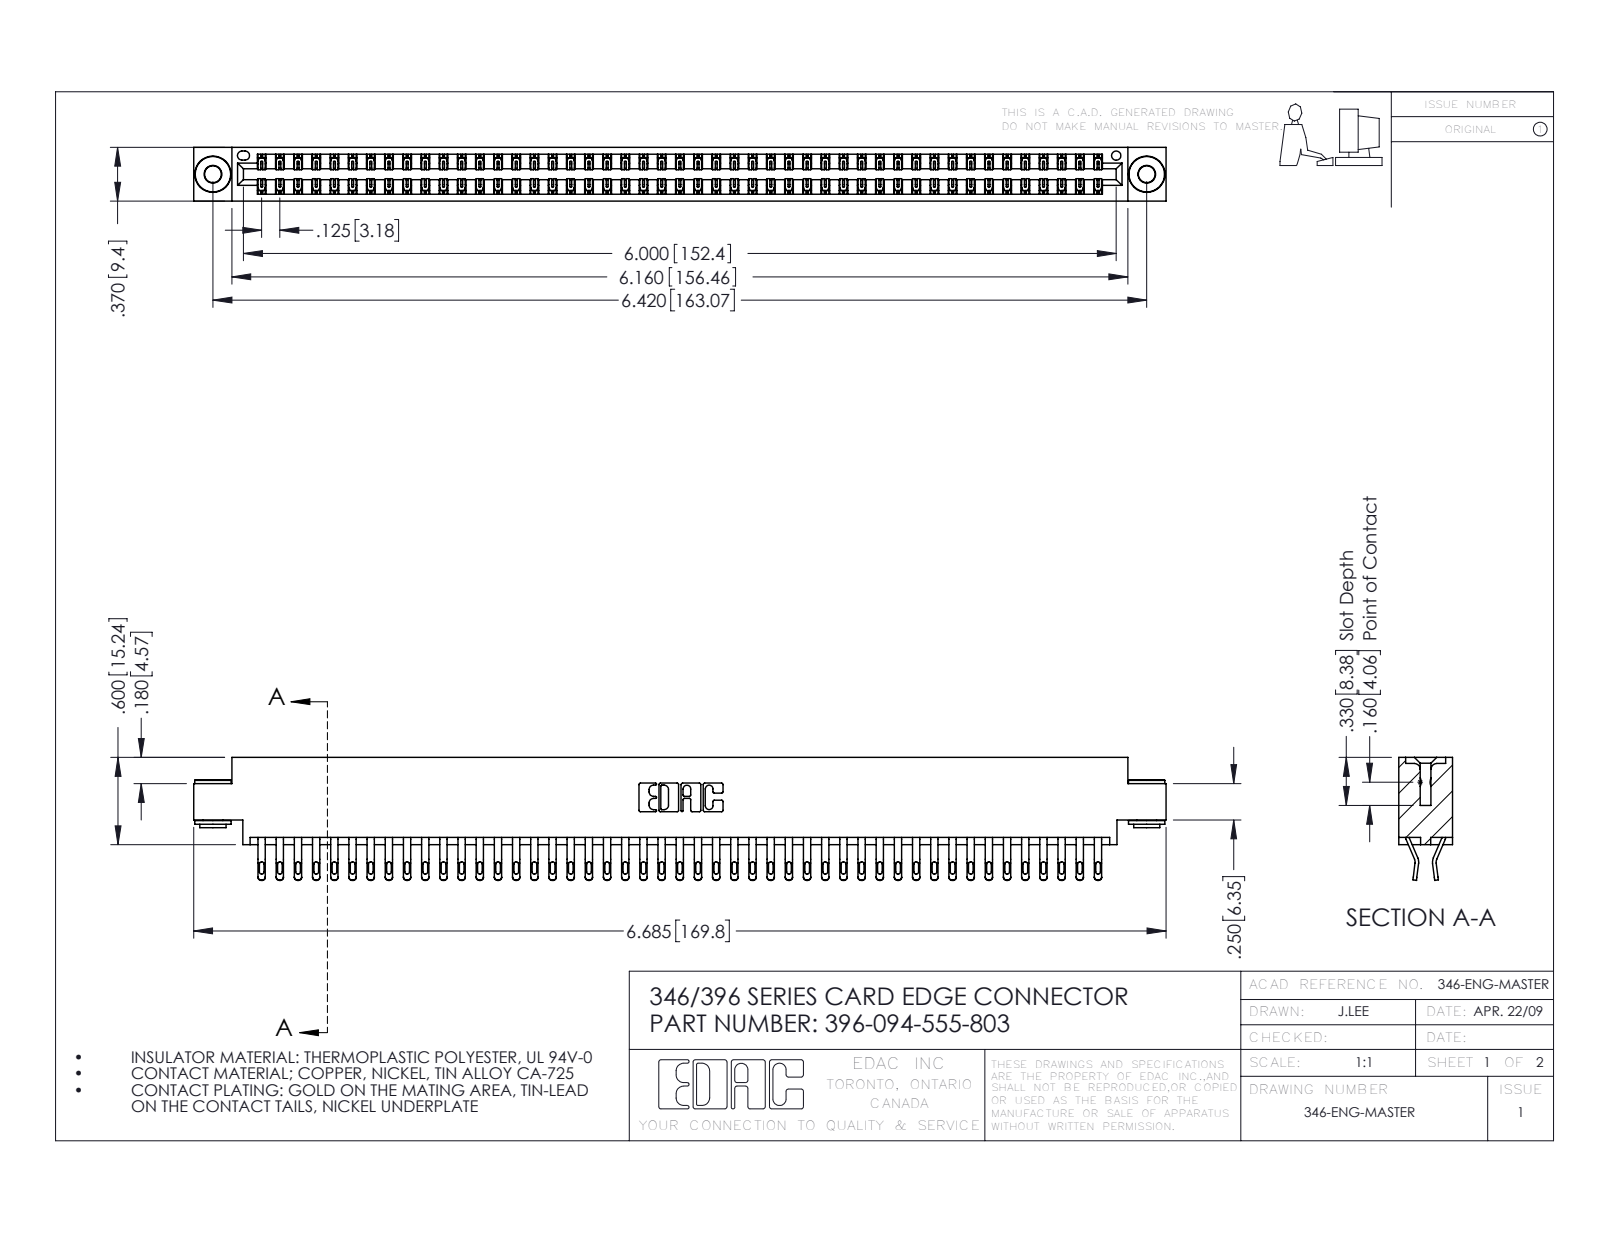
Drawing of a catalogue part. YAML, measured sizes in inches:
part_name: "345-250-002_345-250-002-102; 396-094-555-803; 345-292-001_555 Tail; 346 Part_0.170 Offset - 0.156 Dia-TH"
step_written_by: "SolidWorks 2016 (CONFIG_CONTROL_DESIGN)"
units: inches
bodies: {solids: 97, faces: 5616, planar: 3192, cylindrical: 2416, other: 8}
overall_size: [6.685, 0.845, 0.37]
volume: 1.021
surface_area: 37.89
round_holes:
  - {diameter: 0.116, count: 2}
  - {diameter: 0.156, count: 2}
  - {diameter: 0.064, count: 1}
round_bosses_or_shafts:
  - {diameter: 0.25, count: 2}
  - {diameter: 0.18, count: 2}
  - {diameter: 0.136, count: 2}
partial_cylinders:
  - {radius: 0.016, count: 188}
  - {radius: 0.02, count: 188}
  - {radius: 0.006, count: 141}
  - {radius: 0.01, count: 22}
  - {radius: 0.007, count: 6}
  - {radius: 0.031, count: 6}
  - {radius: 0.026, count: 3}
  - {radius: 0.01, count: 2}
face_to_face_distances: [0.048, 0.322, 0.37, 0.25, 0.025, 0.275, 0.072, 0.298, 0.148, 0.222]
hole_center_spacings: [0.246, 6.211, 6.42]
